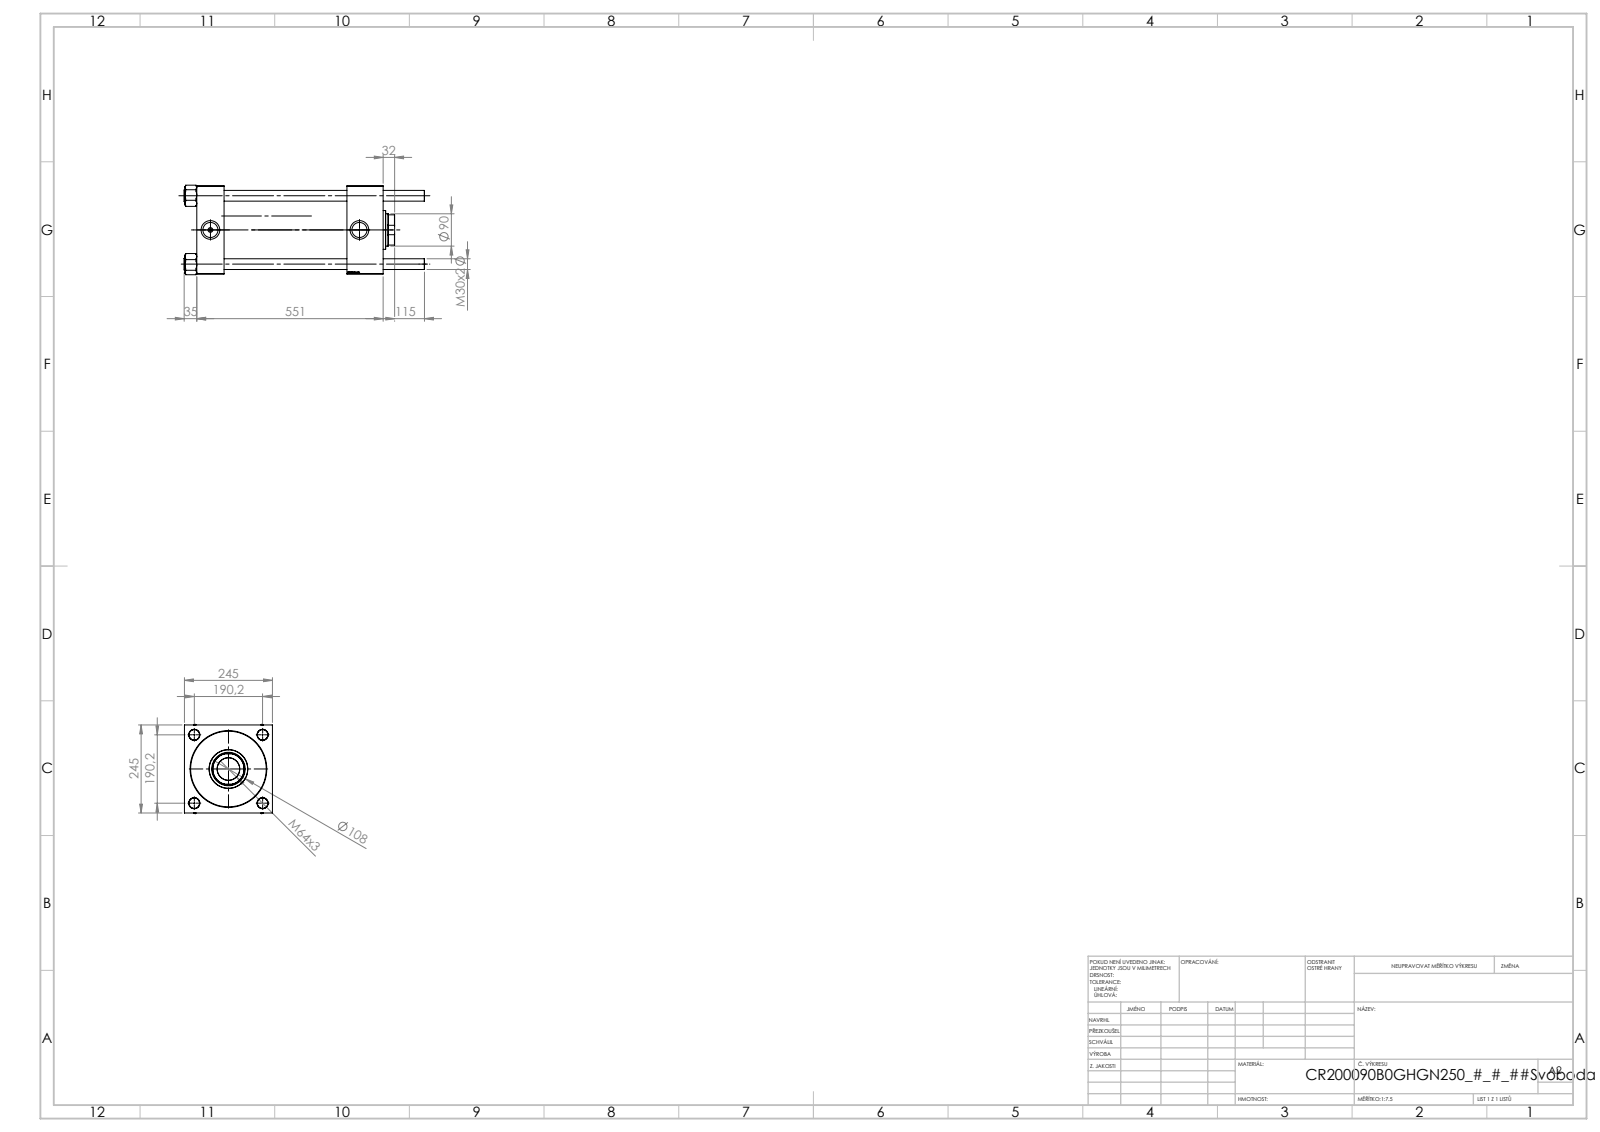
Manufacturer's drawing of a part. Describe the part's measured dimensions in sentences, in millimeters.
The part is named "V215CR_B-1; V215_VC_A; V215CR_VCP_B; NUT_M5_B (+1 more)". Its 3-D file was written by "SolidWorks 2019 (CONFIG_CONTROL_DESIGN)". It is 11 solids with 1206 faces: 480 planar, 78 cylindrical and 648 other. Overall it measures 669 by 249.22 by 245 millimeters. Its volume is 16 480 000 cubic millimeters and its surface area 1 567 000 square millimeters. Round holes: 4 of diameter 30, 2 of diameter 7, 2 of diameter 41.92, 2 of diameter 52, 1 of diameter 62.5, 1 of diameter 90, 1 of diameter 93, 1 of diameter 146, 1 of diameter 200, 1 of diameter 210.5. Round bosses or shafts: 4 of diameter 33, 1 of diameter 206, 1 of diameter 108. Partial cylindrical surfaces (rounded edges, fillets, slot ends): 1 of radius 44. The main face-to-face distances are 245, 76, 519, 443, 490.3, 414.3, 28.7, 101, 418, 342. The hole center spacings are 134.49, 190.2, 268.98, 415.
